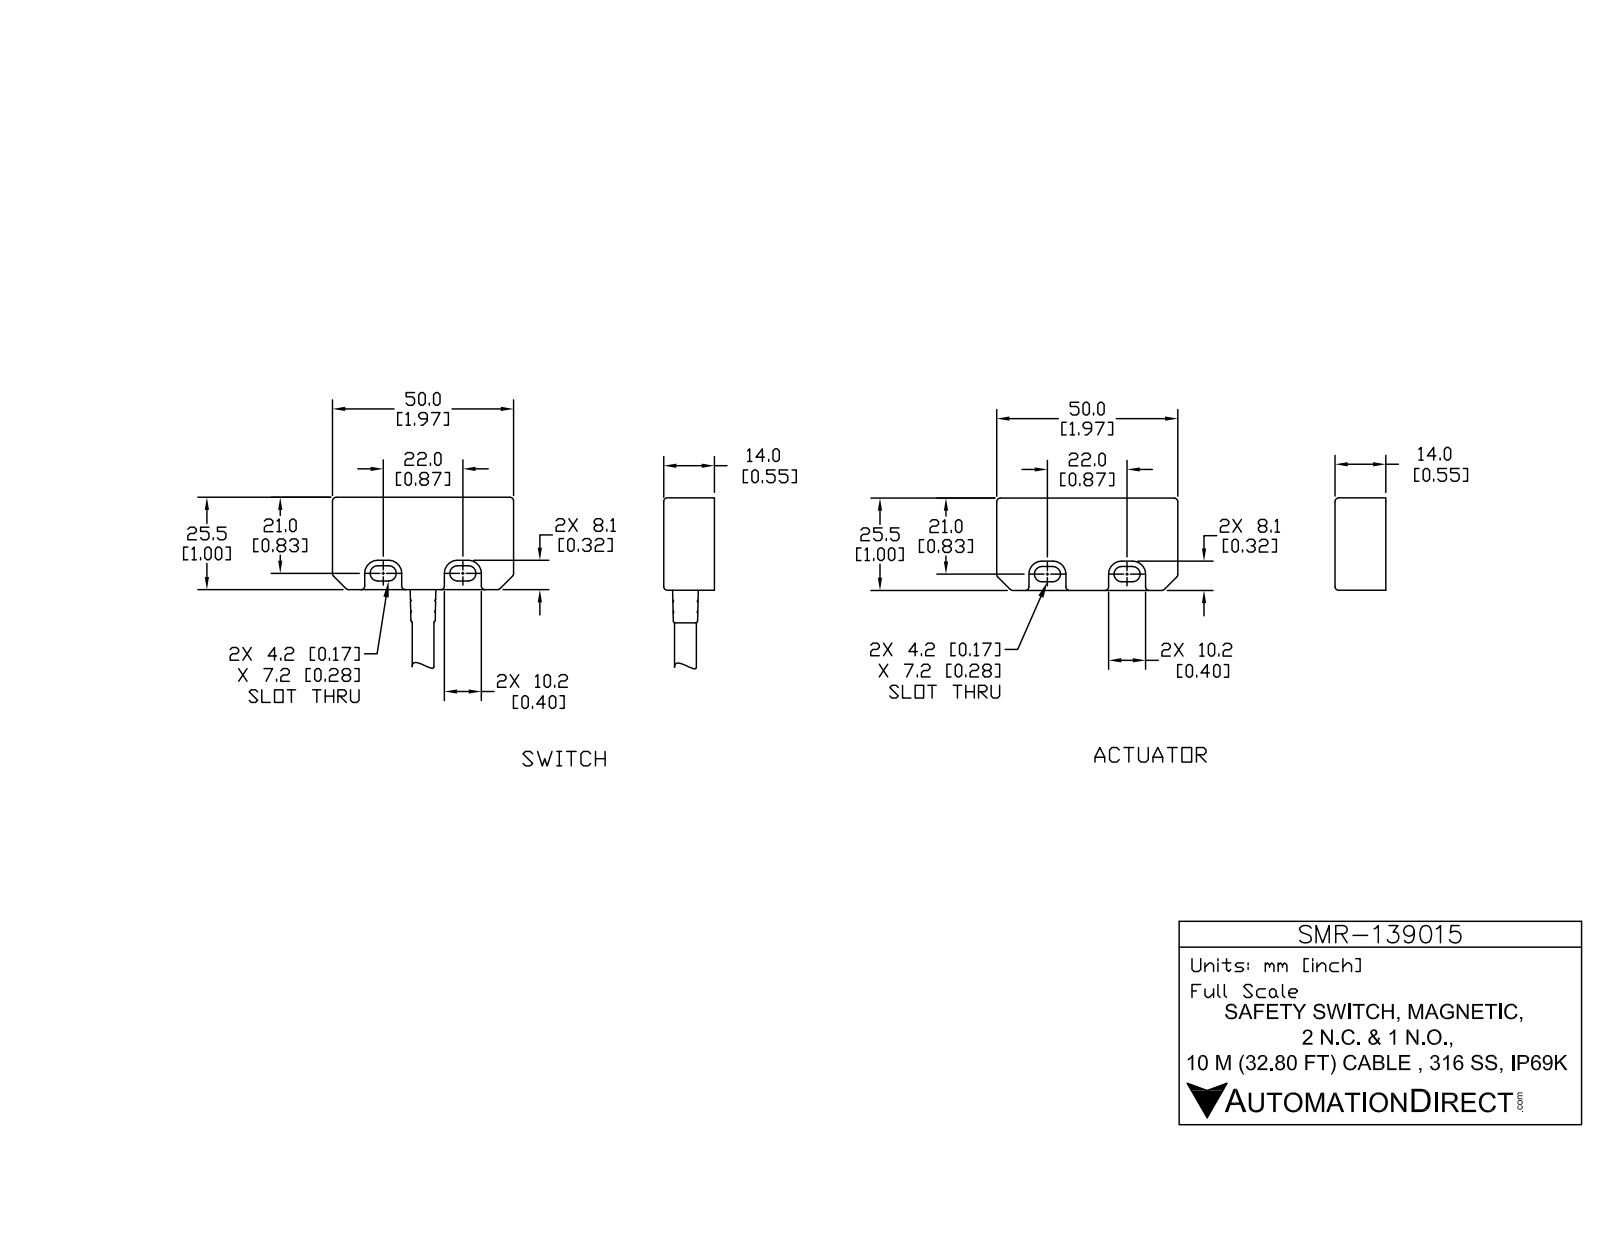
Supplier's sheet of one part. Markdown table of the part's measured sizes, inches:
| quantity | value |
| --- | --- |
| part name | SMR-139015_2; SMR-139015; SMR-139015_1 |
| STEP written by | SolidWorks 2017 (AUTOMOTIVE_DESIGN) |
| units | inches |
| bodies | 4 solids, 201 faces (45 planar, 88 cylindrical, 68 other) |
| overall size | 6.063 × 1.969 × 0.551 |
| volume | 2.184 in³ |
| surface area | 18.53 in² |
| round holes (diameter × count) | 0.287 × 1 |
| round bosses / shafts (diameter × count) | 0.236 × 1 |
| partial cylindrical surfaces (radius × count) | 0.039 × 38, 0.083 × 8, 0.142 × 8, 0.02 × 6 |
| main face-to-face distances | 0.551, 1.004, 1.043, 0.039, 1.969, 2.047, 2.617, 0.177, 0.374, 0.26 |
